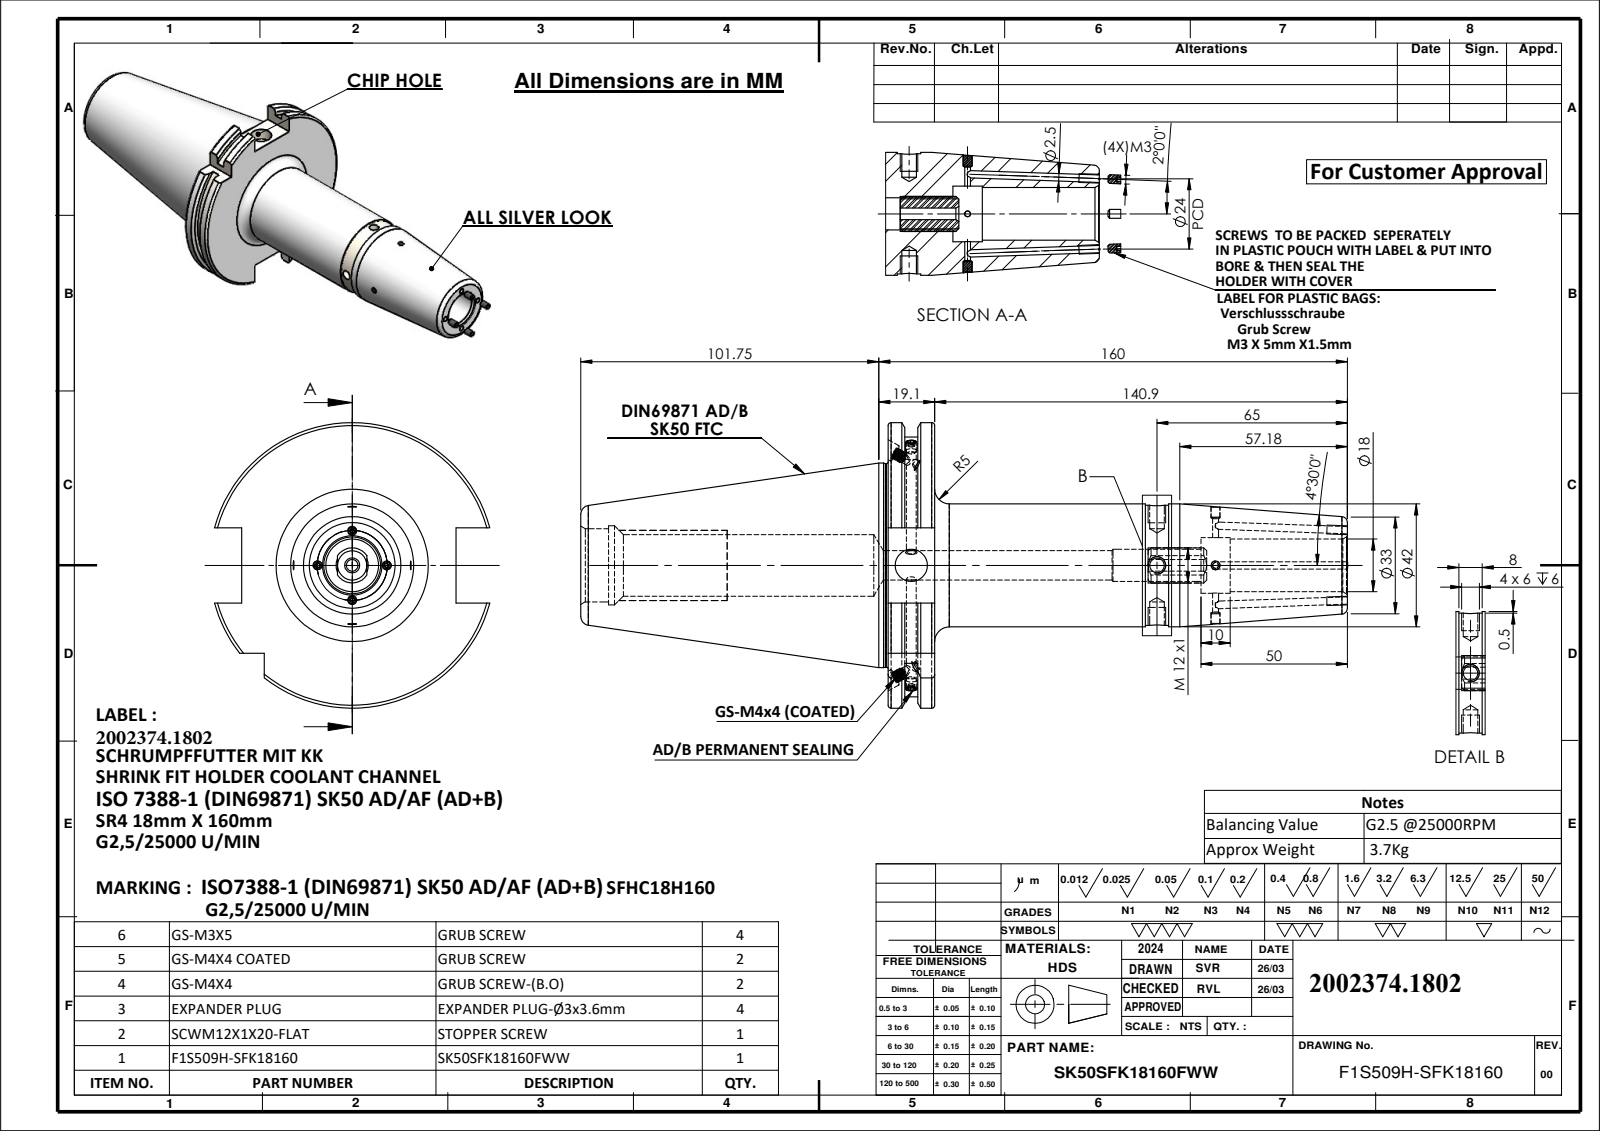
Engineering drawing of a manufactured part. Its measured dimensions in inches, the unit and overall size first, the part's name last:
Units: inches
Overall size (bounding box): 10.622 × 3.839 × 3.703
Round holes (diameter × count): ⌀0.098 ×4, ⌀0.079 ×2, ⌀0.118 ×2, ⌀0.126 ×2, ⌀0.197 ×2, ⌀0.236 ×2, ⌀0.433 ×2, ⌀0.13 ×1, ⌀0.157 ×1, ⌀0.394 ×1, ⌀0.709 ×1, ⌀0.748 ×1
Round bosses / shafts (diameter × count): ⌀0.157 ×4, ⌀0.118 ×4, ⌀0.114 ×2, ⌀2.75 ×1, ⌀2.734 ×1, ⌀1.654 ×1, ⌀1.614 ×1
Partial cylindrical surfaces — rounded edges, fillets, slot ends (radius × count): R0.236 ×1, R1.768 ×1, R1.919 ×1
Main face-to-face distances: 0.626, 0.223, 0.403, 0.399, 0.176, 0.227, 4.132, 4.355, 4.531, 4.758
Hole centre spacings: 0.787, 3.303, 4.091
Volume: 29.44 in³ · Surface area: 110.9 in²
Bodies: 14 solids, 447 faces (133 planar, 134 cylindrical, 180 other)
Part name (STEP PRODUCT): SCWM12X1X20-FLAT; GS-M3X5; F1S509H-SFK18160; GS-M4X4-COATING_DIN 913 - M4 x 4-N (+3 more)
STEP written by: SolidWorks 2024 (AUTOMOTIVE_DESIGN)
